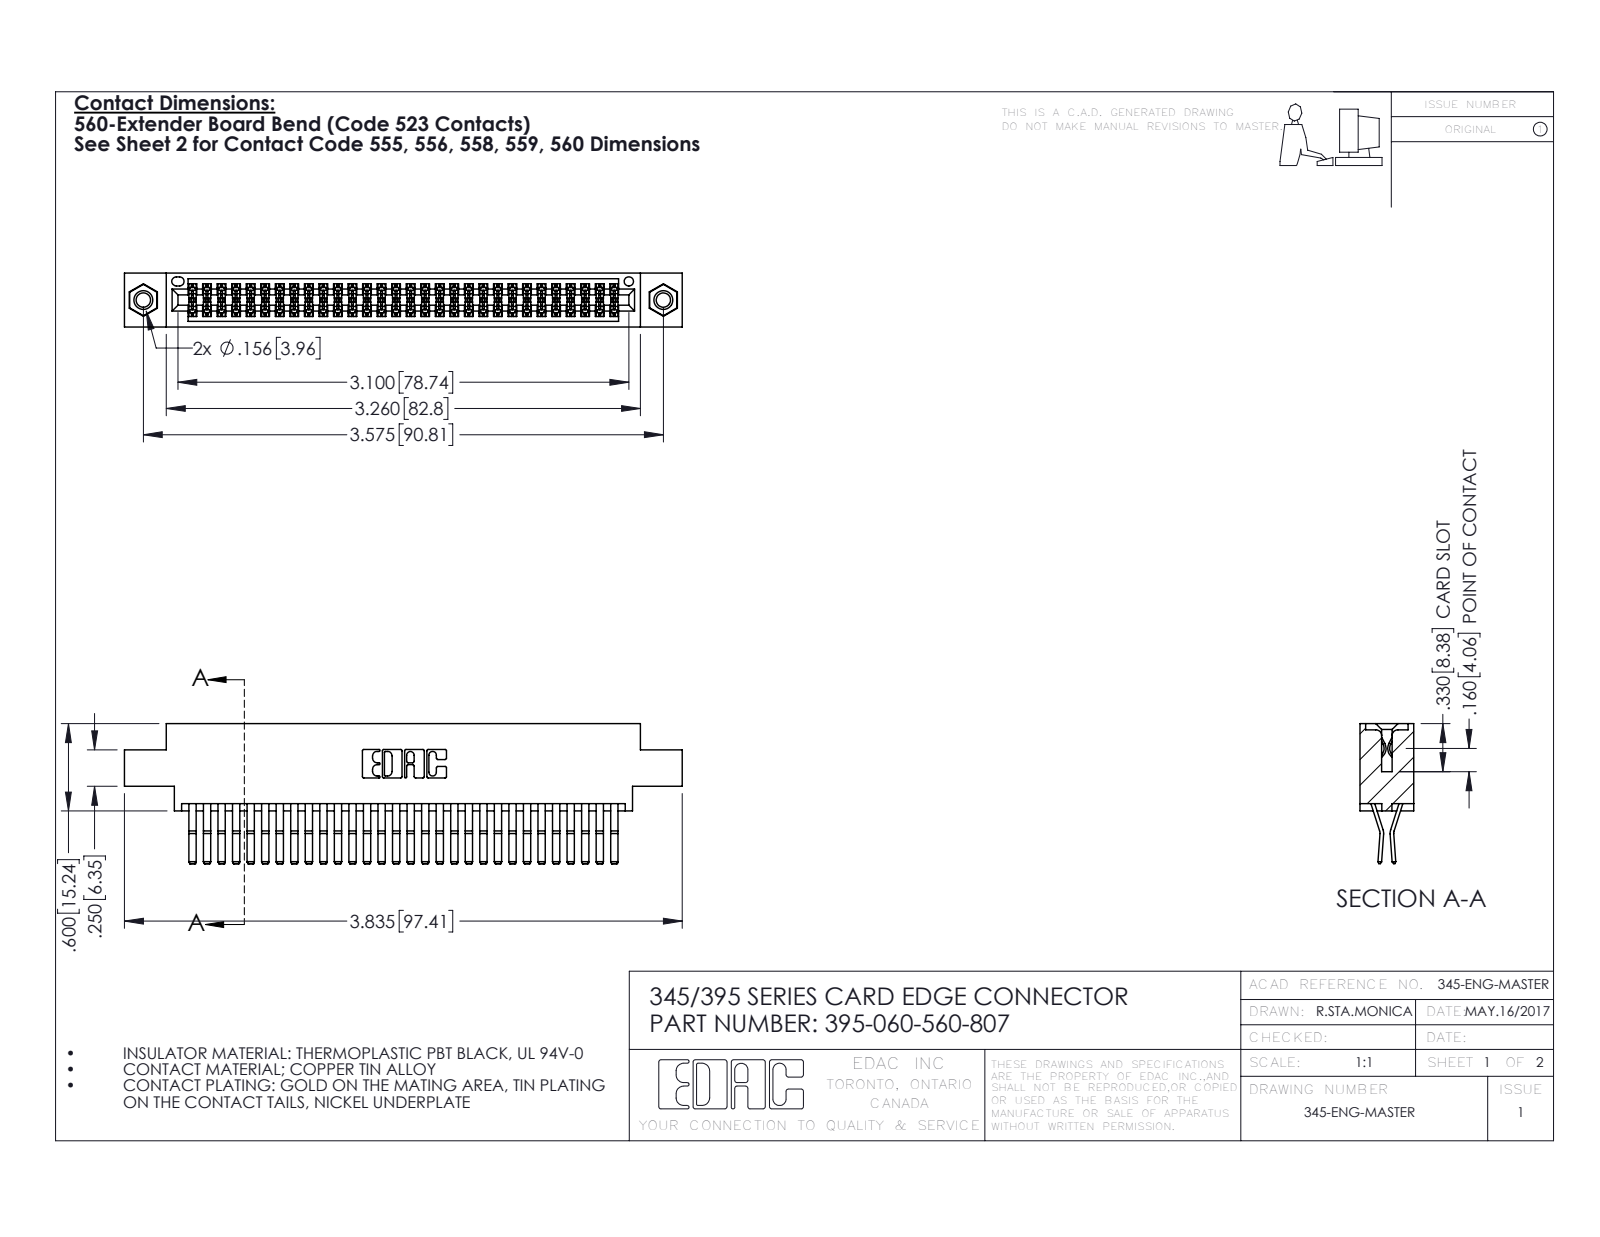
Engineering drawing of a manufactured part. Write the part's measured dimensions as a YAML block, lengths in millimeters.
part_name: "345-250-001_345-250-005-103; 345-292-001_560 Tail; 345 Part_0.170 Offset - 0.156 Dia-TI; 395-060-560-807"
step_written_by: "SolidWorks 2016 (CONFIG_CONTROL_DESIGN)"
units: millimeters
bodies: {solids: 63, faces: 3310, planar: 2096, cylindrical: 1198, other: 16}
overall_size: [97.4, 24.4, 9.4]
volume: 9620
surface_area: 15170
round_holes:
  - {diameter: 2.5, count: 2}
  - {diameter: 3.2, count: 2}
  - {diameter: 4, count: 2}
  - {diameter: 1.6, count: 1}
round_bosses_or_shafts:
  - {diameter: 3.9, count: 2}
partial_cylinders:
  - {radius: 0.2, count: 90}
  - {radius: 0.3, count: 22}
  - {radius: 0.2, count: 6}
  - {radius: 0.8, count: 6}
  - {radius: 0.7, count: 3}
  - {radius: 0.3, count: 2}
  - {radius: 0.4, count: 2}
  - {radius: 0.5, count: 2}
face_to_face_distances: [0.6, 1.8, 7.6, 9.4, 5.1, 2.5, 6.9, 5.7, 4.4, 3.8]
hole_center_spacings: [6.9, 84.8, 90.8]
